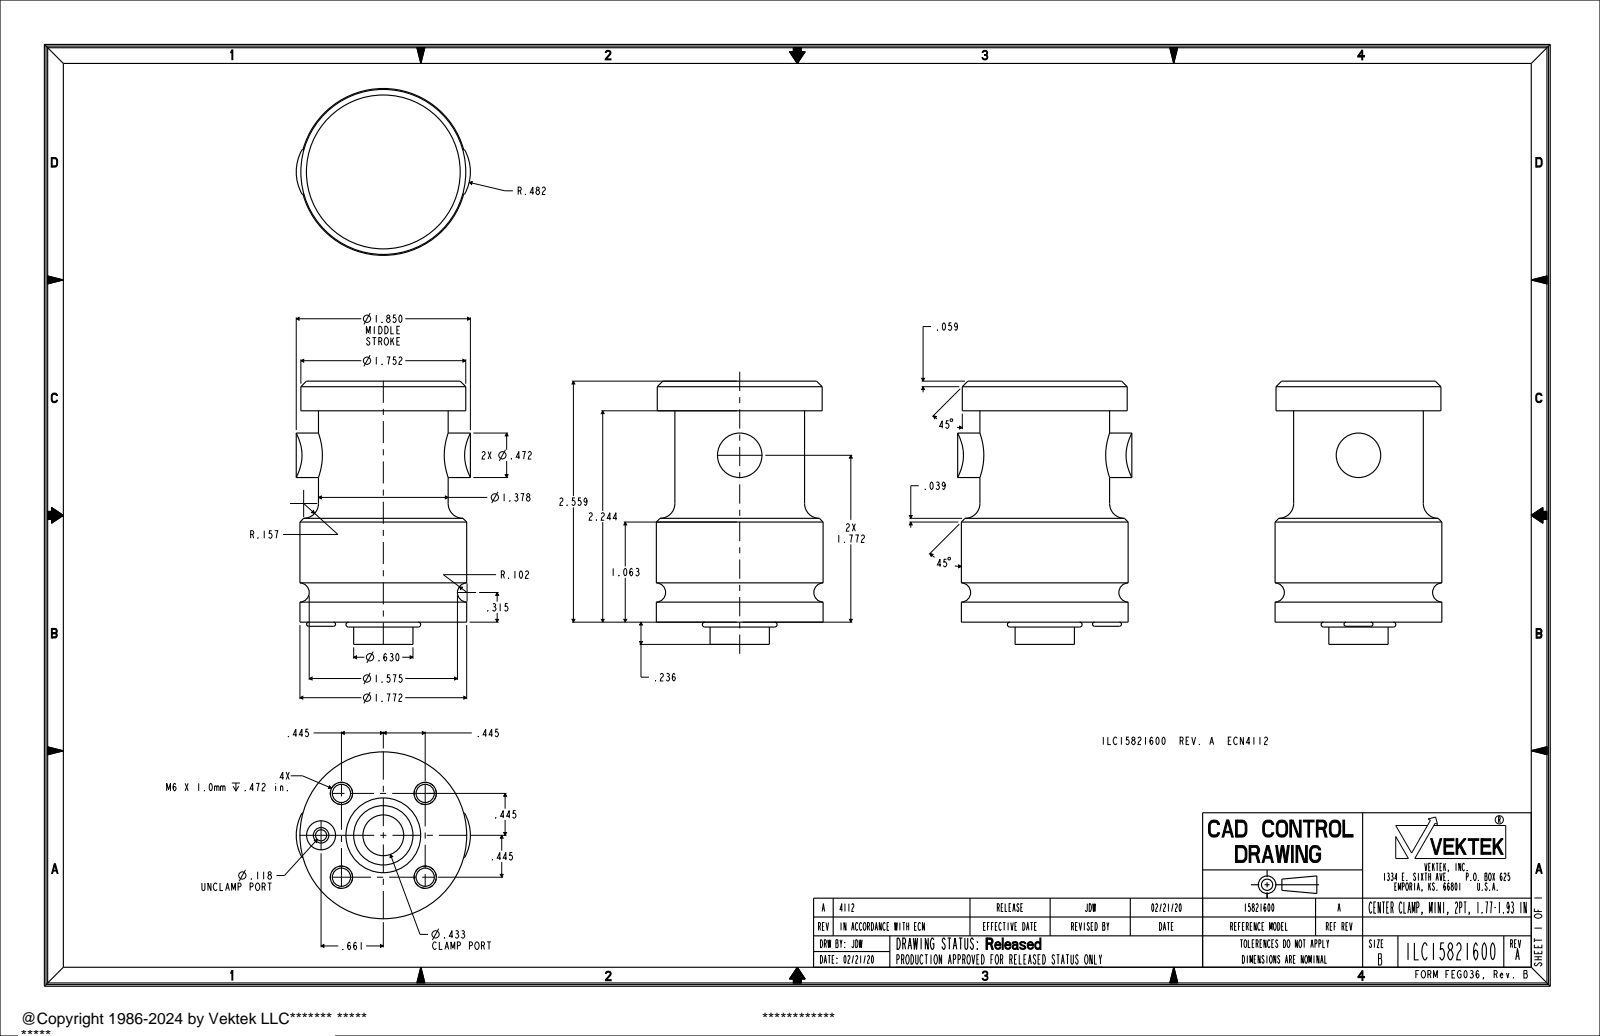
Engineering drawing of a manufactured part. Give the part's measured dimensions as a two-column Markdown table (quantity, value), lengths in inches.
| quantity | value |
| --- | --- |
| part name | ILC15821600 |
| STEP written by | PRO/ENGINEER BY PARAMETRIC TECHNOLOGY CORPORATION, 2013320 (AUTOMOTIVE_DESIGN) |
| units | inches |
| bodies | 1 solid, 86 faces (18 planar, 36 cylindrical, 32 other) |
| overall size | 2.795 × 1.85 × 1.772 |
| volume | 5.175 in³ |
| surface area | 24.33 in² |
| round holes (diameter × count) | 0.194 × 4, 0.118 × 1, 0.433 × 1 |
| round bosses / shafts (diameter × count) | 0.236 × 4, 1.772 × 1, 1.752 × 1, 1.378 × 1, 0.63 × 1, 0.472 × 1 |
| partial cylindrical surfaces (radius × count) | 0.482 × 2 |
| main face-to-face distances | 2.559, 0.315, 2.244, 2.48, 0.236, 2.795, 0.197, 0.039, 2.283, 2.598 |
| hole center spacings | 0.629, 0.89, 0.495, 1.193, 1.258, 0.661 |
